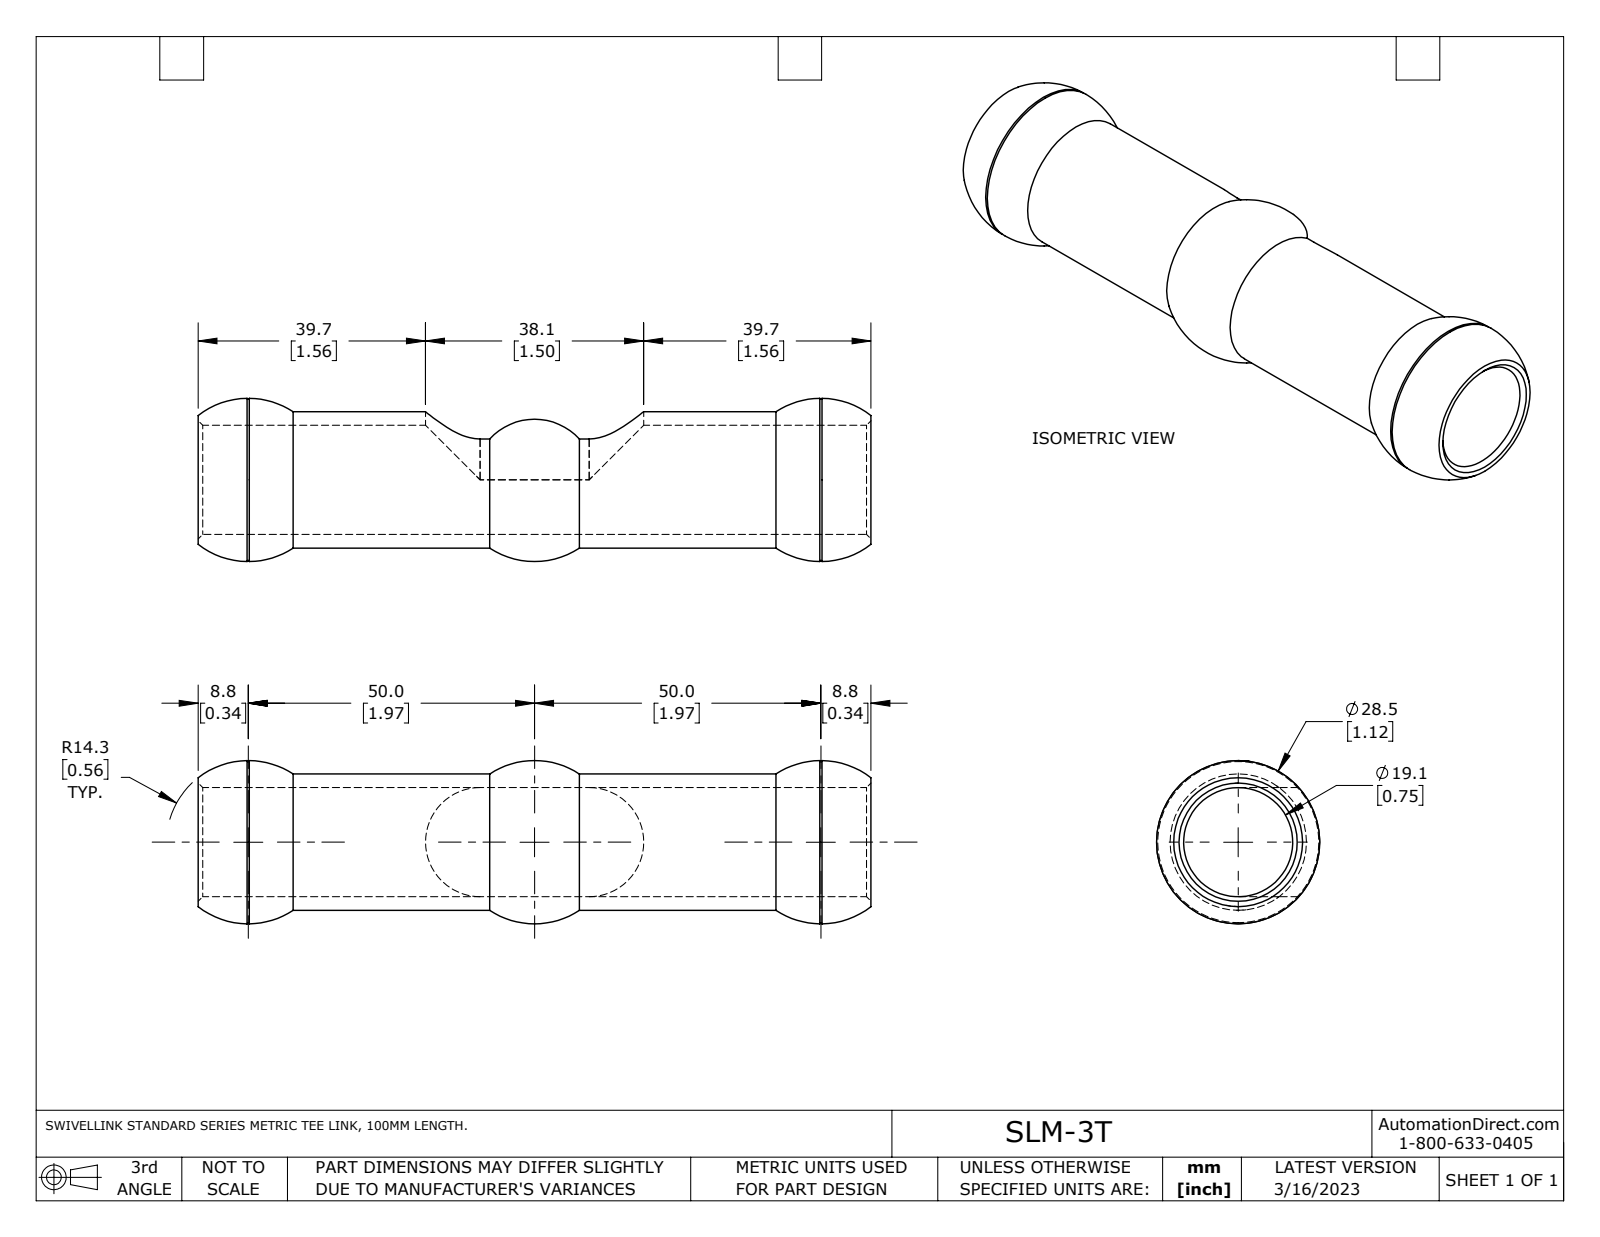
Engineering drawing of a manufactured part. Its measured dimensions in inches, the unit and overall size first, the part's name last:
Units: inches
Overall size (bounding box): 4.626 × 1.122 × 1.122
Round holes (diameter × count): ⌀0.75 ×1
Round bosses / shafts (diameter × count): ⌀0.937 ×1
Partial cylindrical surfaces — rounded edges, fillets, slot ends (radius × count): R0.375 ×2
Main face-to-face distances: 0.75, 4.626
Volume: 0.6 in³ · Surface area: 24.94 in²
Bodies: 1 solid, 18 faces (4 planar, 5 cylindrical, 9 other)
Part name (STEP PRODUCT): SLM-3T
STEP written by: SolidWorks 2021 (AUTOMOTIVE_DESIGN)
